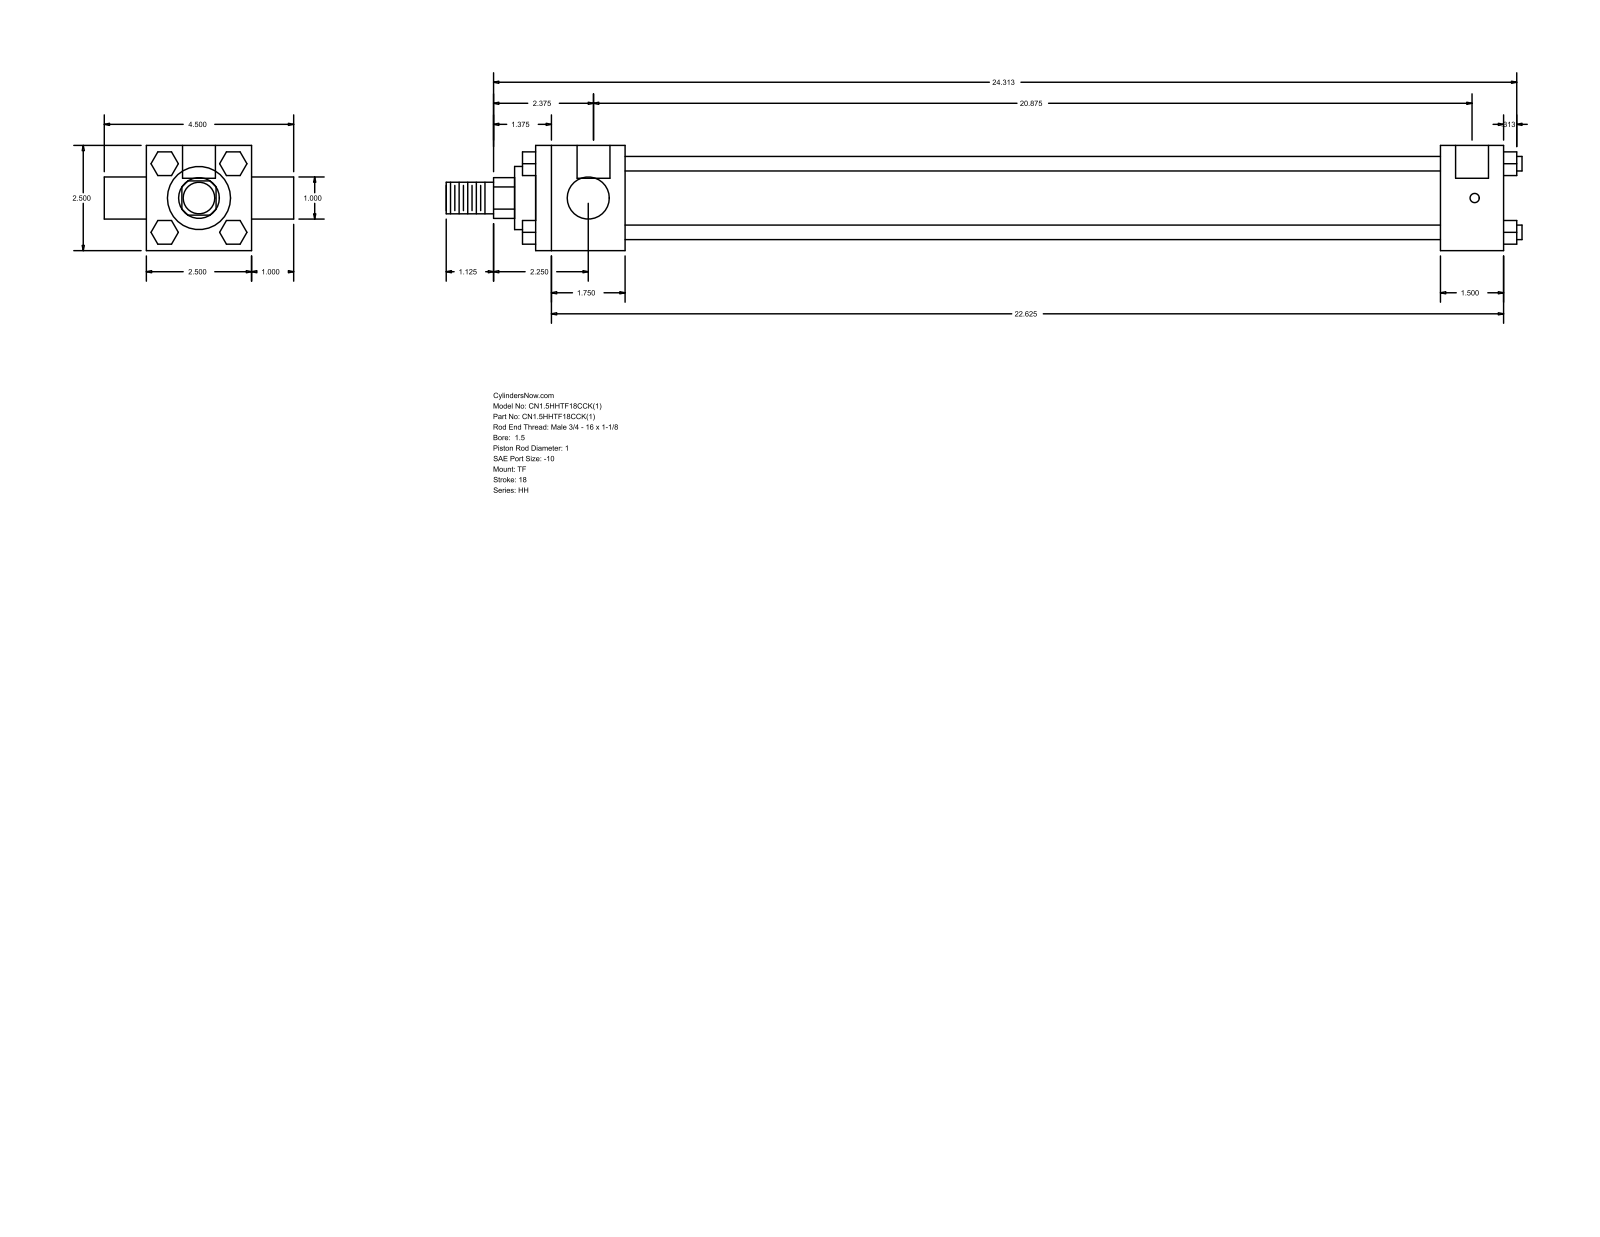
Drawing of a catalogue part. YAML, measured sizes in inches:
part_name: "HH_TF__0150_1"
step_written_by: "GSSL Pune (CONFIG_CONTROL_DESIGN)"
units: inches
bodies: {solids: 0, faces: 120, planar: 92, cylindrical: 28, other: 0}
overall_size: [25.563, 4.5, 2.5]
round_holes:
  - {diameter: 0.219, count: 3}
  - {diameter: 0.781, count: 2}
round_bosses_or_shafts:
  - {diameter: 0.345, count: 4}
  - {diameter: 1, count: 2}
  - {diameter: 1.75, count: 1}
  - {diameter: 1.5, count: 1}
  - {diameter: 0.75, count: 1}
partial_cylinders:
  - {radius: 0.484, count: 1}
face_to_face_distances: [2.5, 1.5, 20.875, 19.375, 2.125, 21.5, 23, 1, 0.815, 0.563]
hole_center_spacings: [0.063, 20.937, 20.875, 21]
